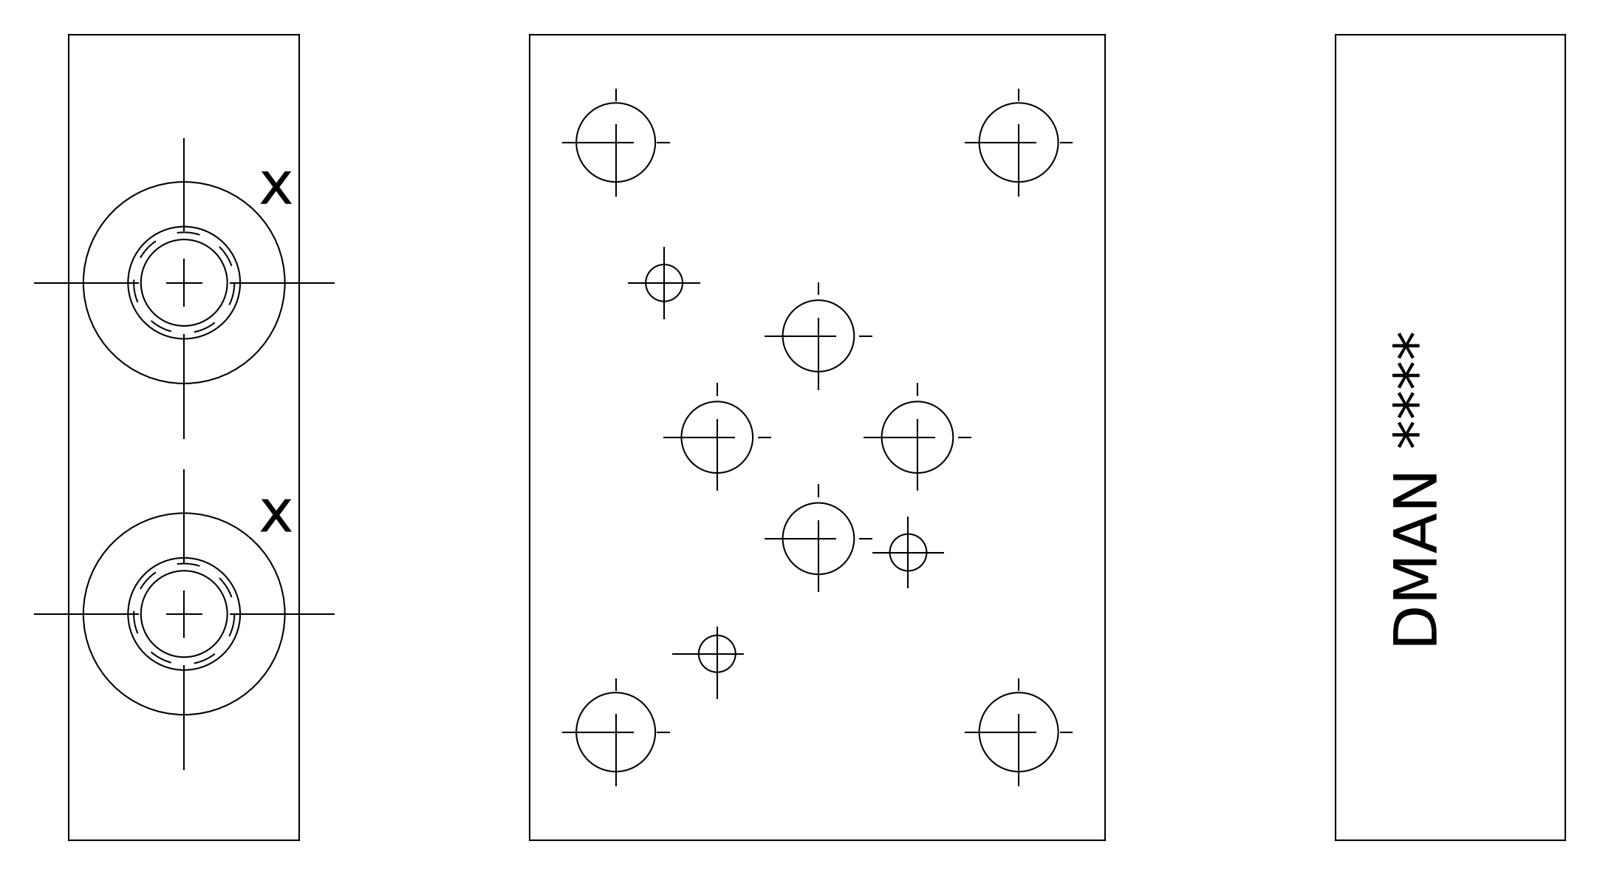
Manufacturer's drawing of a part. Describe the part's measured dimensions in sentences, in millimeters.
The part is named "Part_AS04TPX4S_3D". Its 3-D file was written by "Autodesk Inventor 2019 (AUTOMOTIVE_DESIGN)". It is 1 solid with 390 faces: 270 planar, 32 cylindrical and 88 other. Overall it measures 88.9 by 63.5 by 25.4 millimeters. Its volume is 136 006 cubic millimeters and its surface area 22 083 square millimeters. Round holes: 4 of diameter 7.92, 4 of diameter 8.33, 4 of diameter 14.27, 2 of diameter 9.53, 2 of diameter 9.88, 2 of diameter 11.13, 2 of diameter 21.29, 1 of diameter 3.17, 1 of diameter 3.96, 1 of diameter 4.01. The main face-to-face distances are 25.4, 63.5, 88.9, 0.79, 62.71, 1.27, 24.13, 1, 87.9, 11.5. The hole center spacings are 15.72, 22.23, 30.86, 30.88, 34.38, 34.39, 44.45, 46.57.
